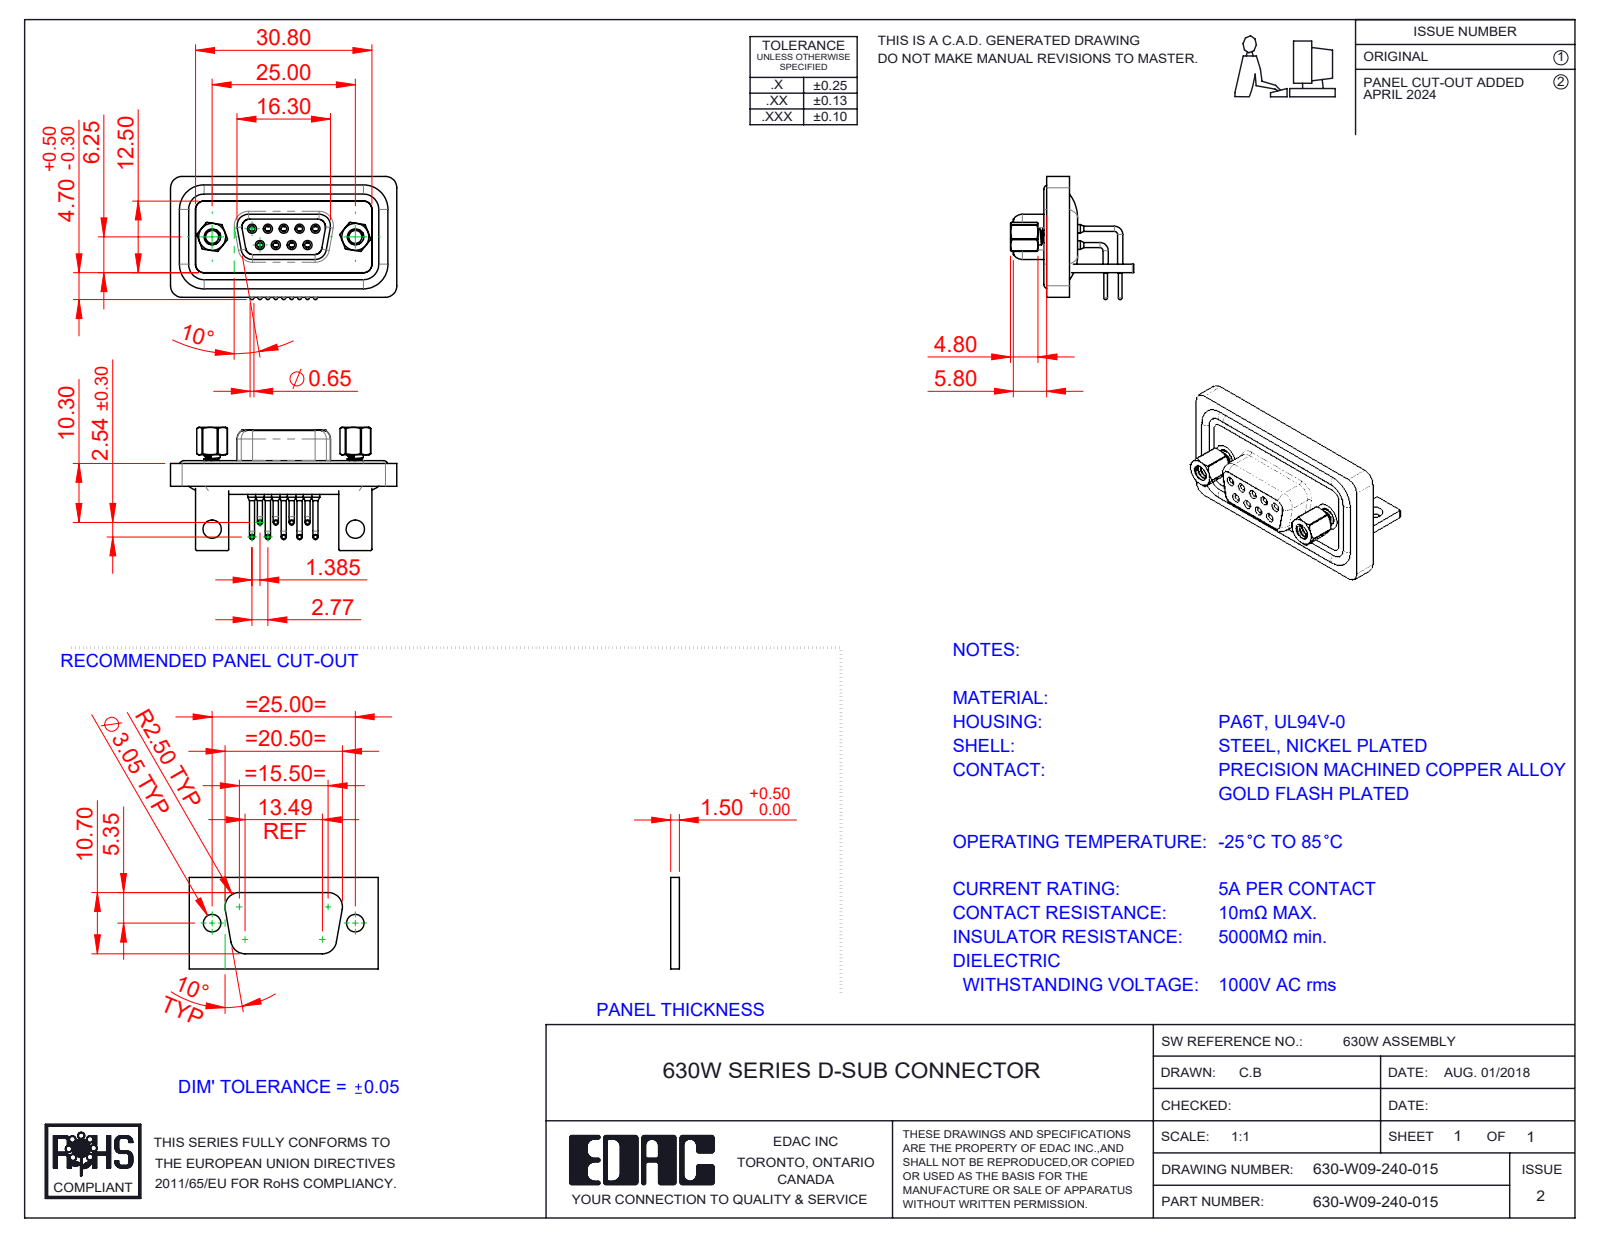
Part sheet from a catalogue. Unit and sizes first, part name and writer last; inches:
Units: inches
Overall size (bounding box): 1.556 × 0.846 × 0.846
Round holes (diameter × count): ⌀0.039 ×9, ⌀0.043 ×9, ⌀0.059 ×9, ⌀0.067 ×9, ⌀0.071 ×9, ⌀0.079 ×9, ⌀0.089 ×2, ⌀0.09 ×2, ⌀0.126 ×2, ⌀0.157 ×2, ⌀0.189 ×2, ⌀0.193 ×2
Round bosses / shafts (diameter × count): ⌀0.035 ×18, ⌀0.063 ×13, ⌀0.026 ×9, ⌀0.059 ×4, ⌀0.11 ×2, ⌀0.197 ×1
Partial cylindrical surfaces — rounded edges, fillets, slot ends (radius × count): R0.079 ×15, R0.059 ×14, R0.01 ×12, R0.053 ×8, R0.106 ×6, R0.02 ×5, R0.035 ×4, R0.063 ×4
Main face-to-face distances: 0.016, 0.063, 0.043, 0.071, 0.169, 0.114, 0.098, 0.059, 0.228, 0.02
Hole centre spacings: 0.124, 0.109, 0.218, 0.198, 0.198, 0.294, 0.295, 0.327
Volume: 0.287 in³ · Surface area: 12.49 in²
Bodies: 19 solids, 966 faces (258 planar, 469 cylindrical, 239 other)
Part name (STEP PRODUCT): 630W 4-40 Threaded Rivet_Stabilizer; 630-W09-240-015; 630W Shell_09 Contacts; 630W Contact Row 1 (+5 more)
STEP written by: SolidWorks 2023 (CONFIG_CONTROL_DESIGN)
